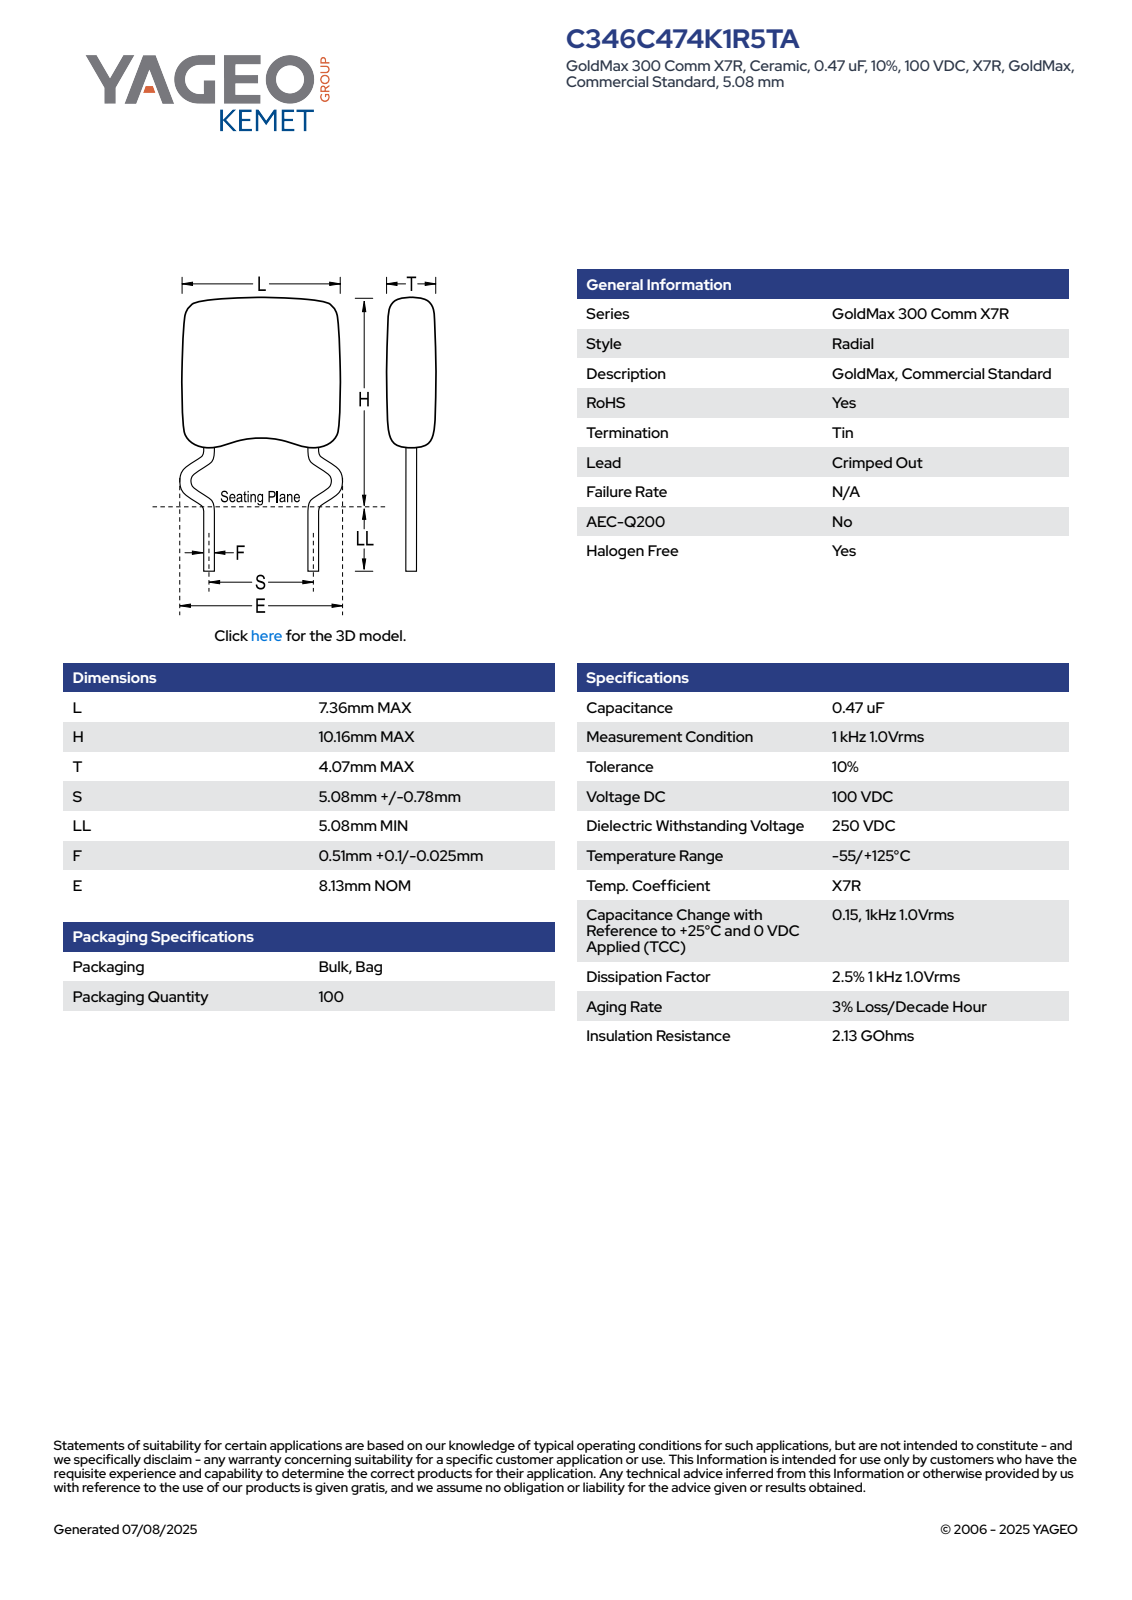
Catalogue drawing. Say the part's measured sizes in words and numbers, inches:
The part is named "CCR_RCCR_C346_L7.36H10.16T4.07S5.08LL5.08F0.51E8.13". Its 3-D file was written by "SolidWorks 2014 (AUTOMOTIVE_DESIGN)". It is 4 solids with 104 faces: 66 planar, 16 cylindrical and 22 other. Overall it measures 0.6 by 0.32 by 0.161 inches. Its volume is 0.011 cubic inches and its surface area 0.353 square inches. Round bosses or shafts: 2 of diameter 0.02. Partial cylindrical surfaces (rounded edges, fillets, slot ends): 8 of radius 0.015, 4 of radius 0.03. The main face-to-face distances are 0.16, 0.29, 0.252, 0.161, 0.348, 0.6, 0.496, 0.148, 0.104, 0.45.
